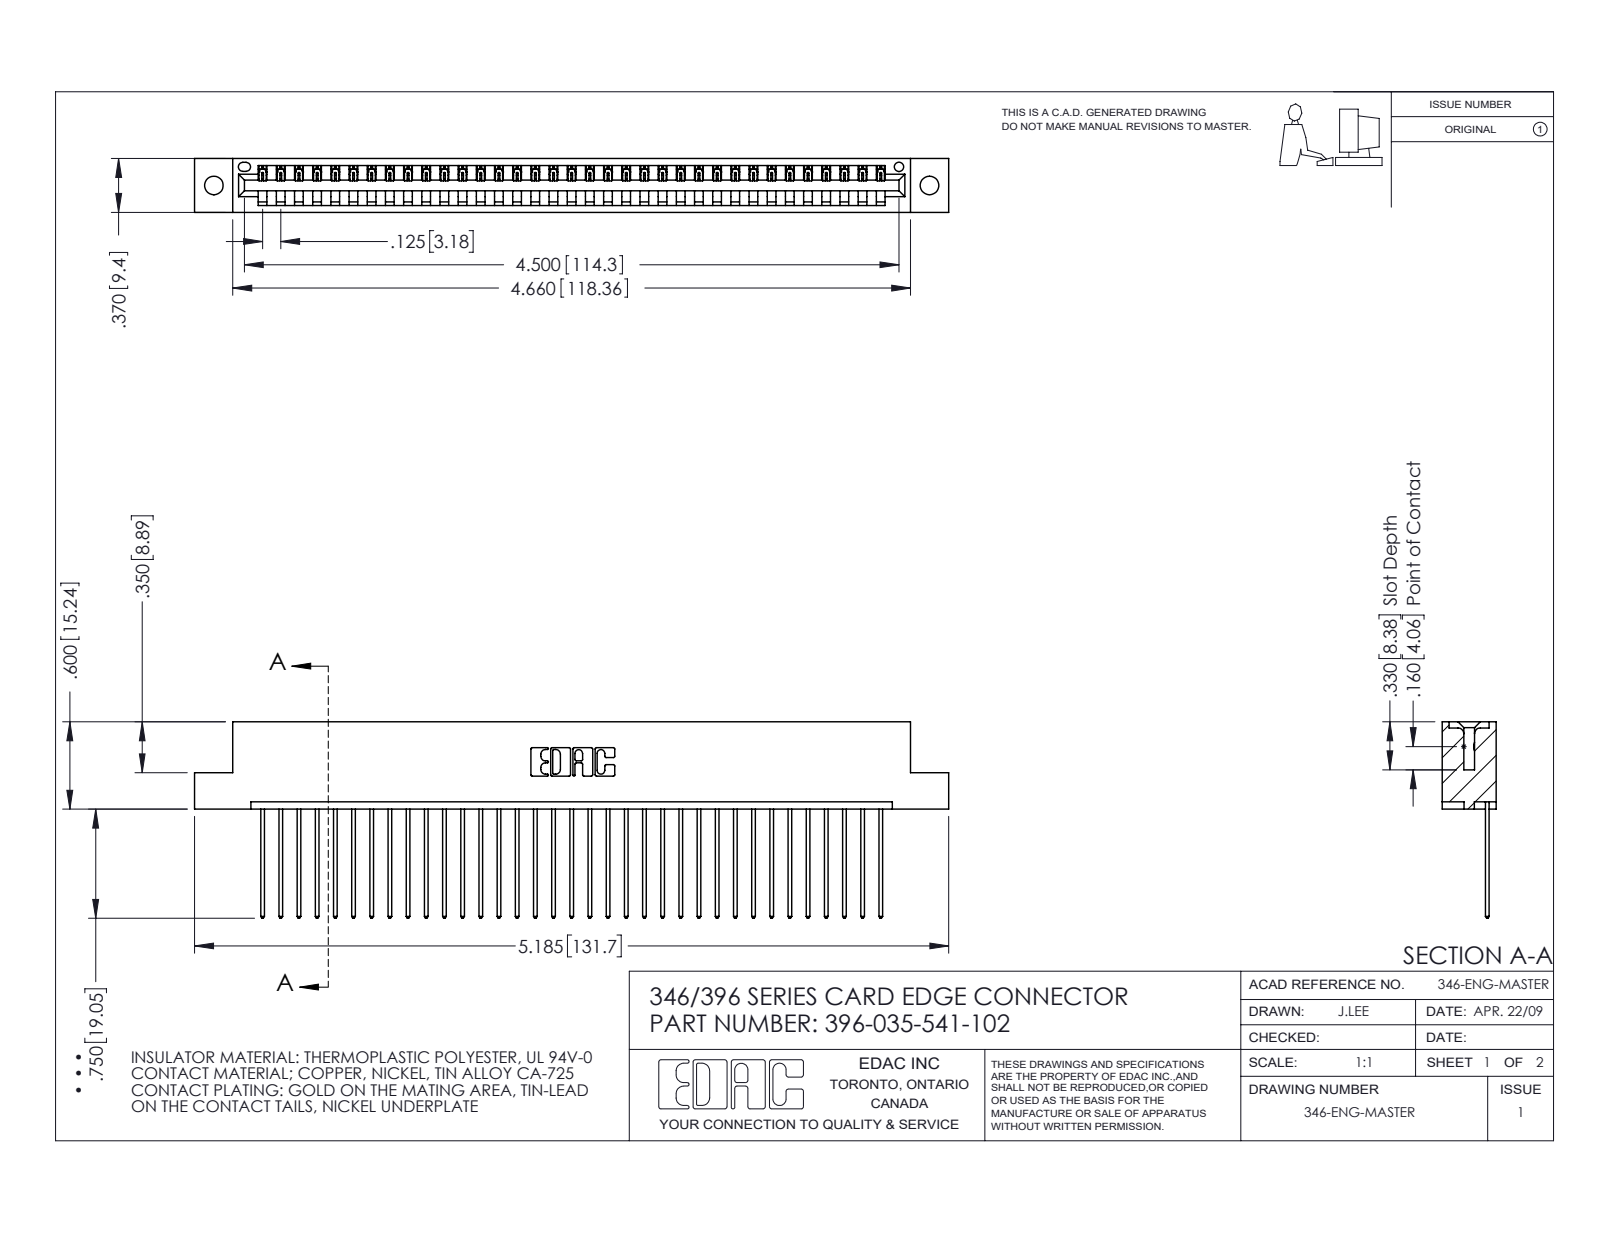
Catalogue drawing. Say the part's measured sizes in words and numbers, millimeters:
The part is named "396-035-541-102; 345-292-001_345-293-141; 346 Part_Flush Mounting Lugs - 0.128 Dia". Its 3-D file was written by "SolidWorks 2016 (CONFIG_CONTROL_DESIGN)". It is 36 solids with 2152 faces: 1476 planar, 676 cylindrical and 0 other. Overall it measures 131.7 by 34.3 by 9.4 millimeters. Its volume is 12 600 cubic millimeters and its surface area 16 140 square millimeters. Round holes: 2 of diameter 3.3, 1 of diameter 1.6. Partial cylindrical surfaces (rounded edges, fillets, slot ends): 70 of radius 0.2, 70 of radius 0.3, 22 of radius 0.3, 6 of radius 0.2, 6 of radius 0.8, 3 of radius 0.7, 2 of radius 0.8, 2 of radius 1. The main face-to-face distances are 1.2, 8.2, 9.4, 6.4, 1.8, 7.6, 0.6, 3.8, 5.6, 2.5. The hole center spacings are 6.2, 119.7, 125.
